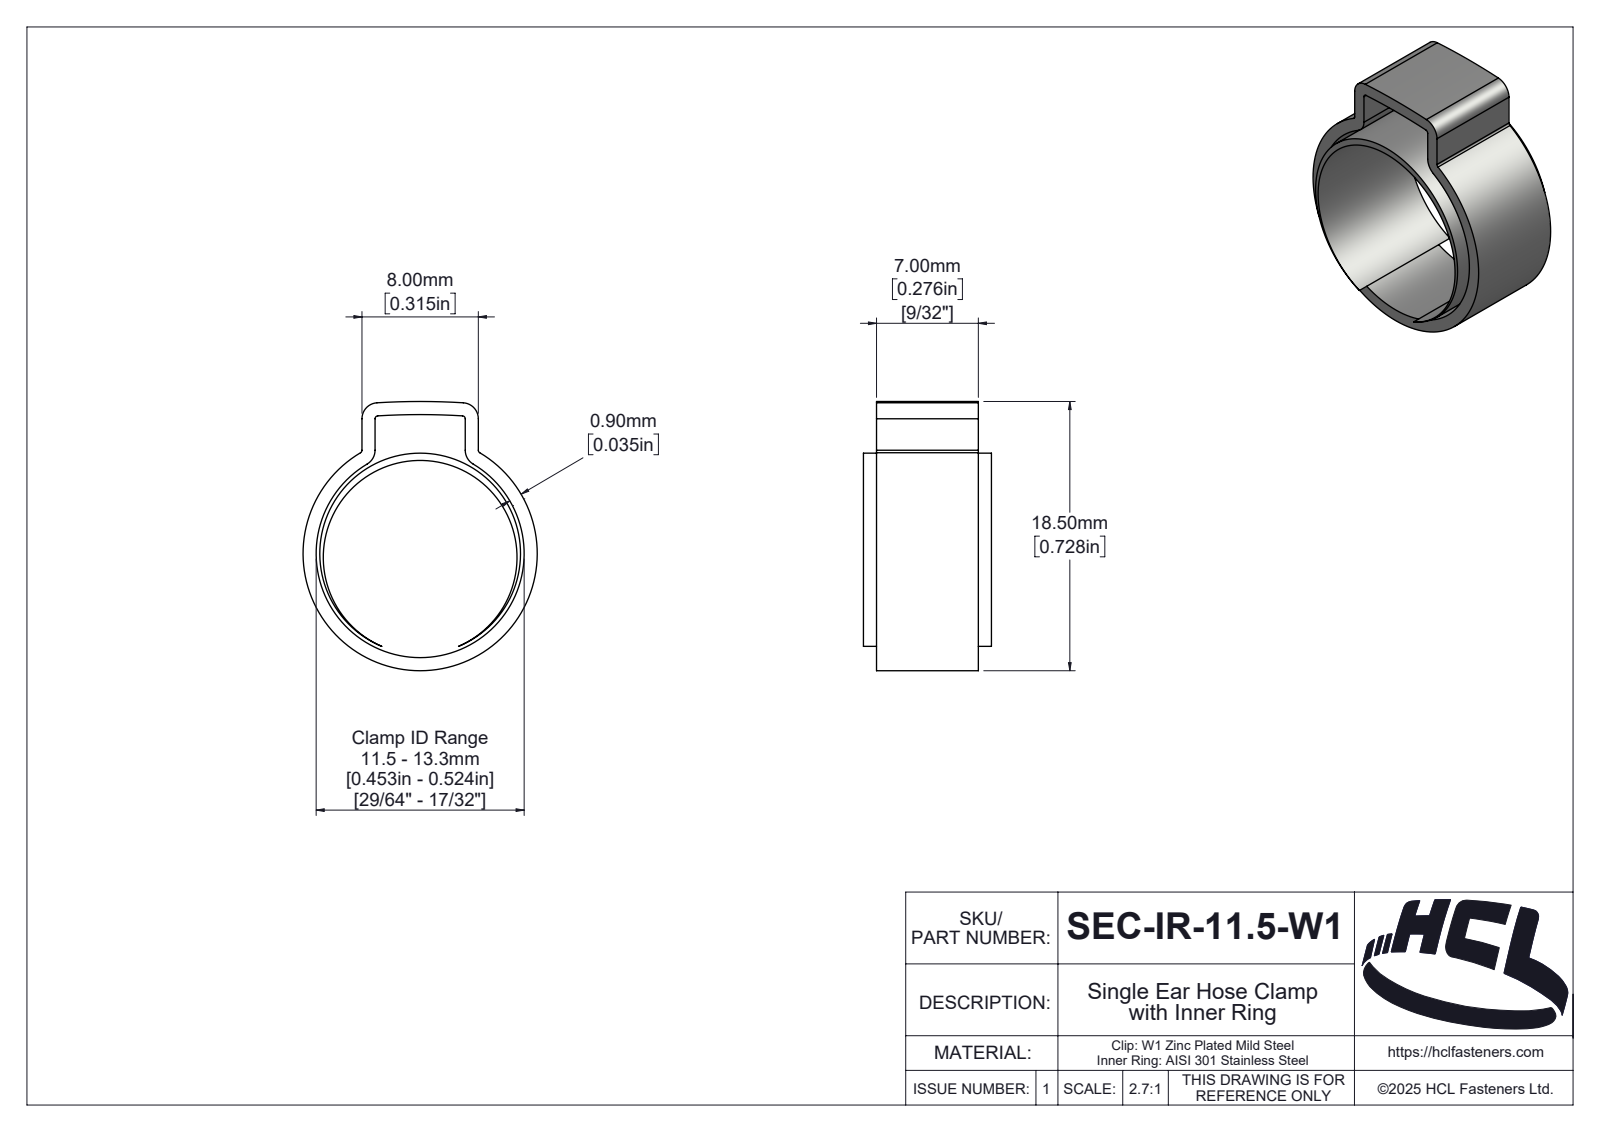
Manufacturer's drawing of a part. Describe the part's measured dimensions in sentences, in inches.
The part is named "SEC-IR-11.5-W1". Its 3-D file was written by "SolidWorks 2025 (AUTOMOTIVE_DESIGN)". It is 2 solids with 131 faces: 10 planar, 72 cylindrical and 49 other. Overall it measures 0.728 by 0.634 by 0.346 inches. Its volume is 0.026 cubic inches and its surface area 2.353 square inches. Round holes: 1 of diameter 0.524, 1 of diameter 0.563. Round bosses or shafts: 1 of diameter 0.634, 1 of diameter 0.543. Partial cylindrical surfaces (rounded edges, fillets, slot ends): 4 of radius 0.008, 4 of radius 0.043, 1 of radius 0.008, 1 of radius 0.032, 1 of radius 0.04, 1 of radius 0.042, 1 of radius 0.05, 1 of radius 0.071. The main face-to-face distances are 0.035, 0.276, 0.28, 0.311, 0.315, 0.244, 0.346, 0.147, 0.111, 0.133.
